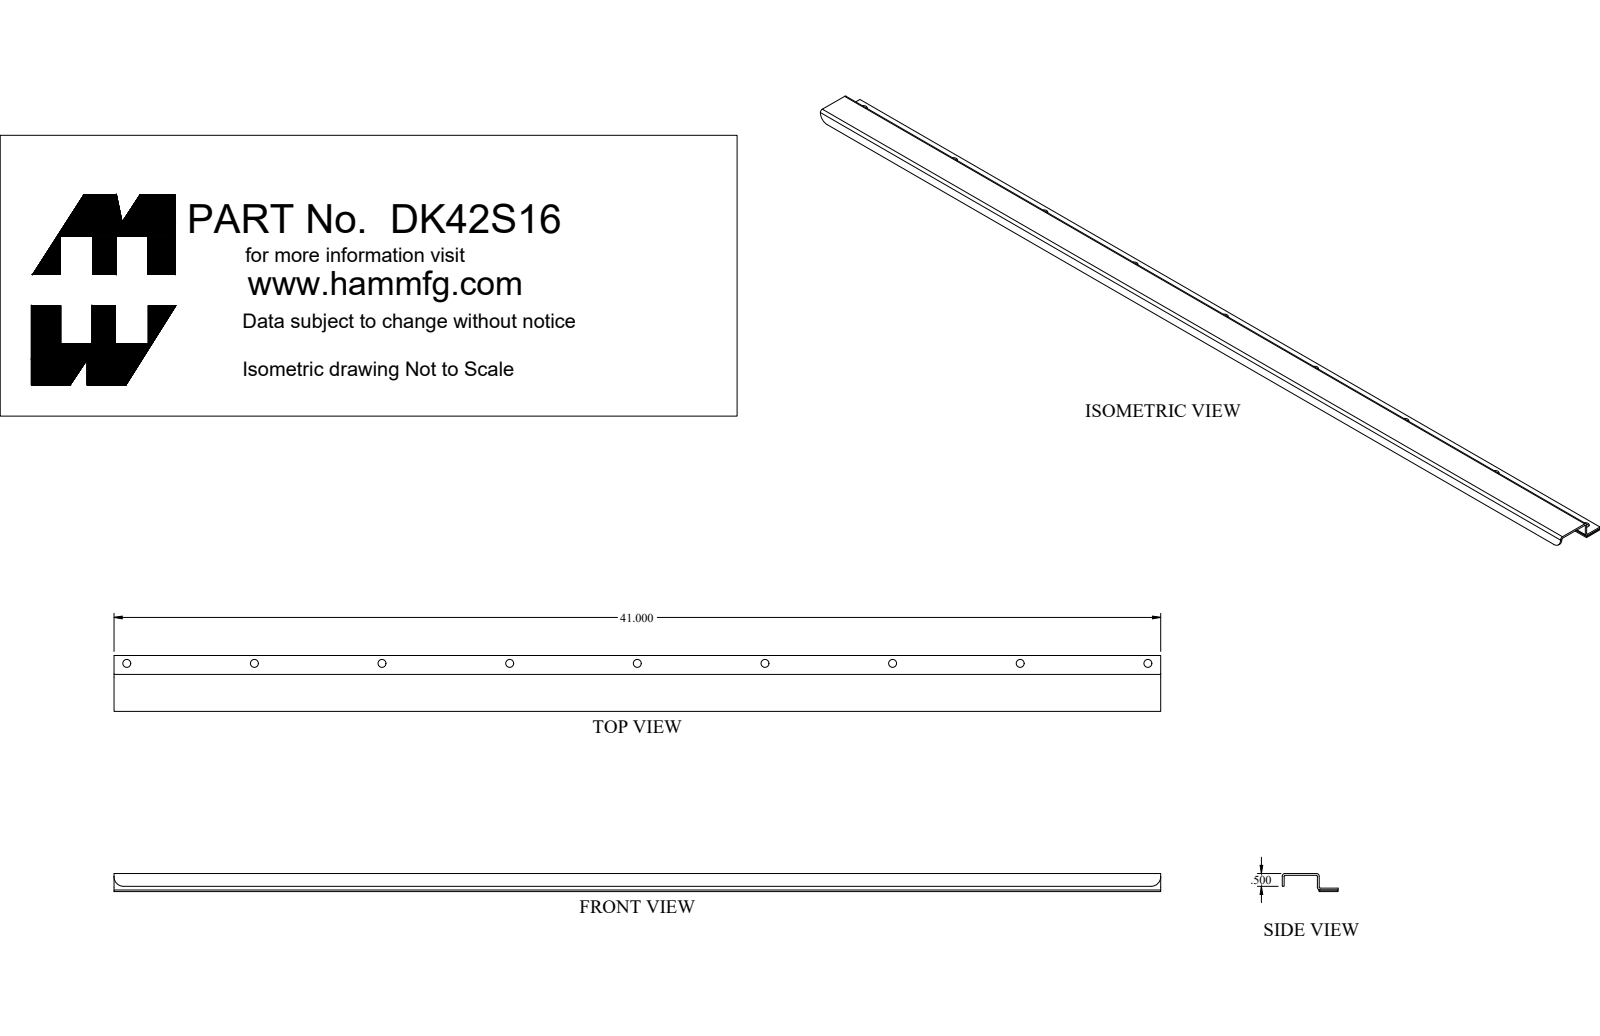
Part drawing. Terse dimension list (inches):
name: DK42S16
written by: SolidWorks 2021 (AUTOMOTIVE_DESIGN)
unit: in
bodies: 5 solids, 70 faces (47 planar, 22 cylindrical, 1 other)
size: 41 × 2.188 × 1.322
volume: 11.11 in³; area: 328.6 in²
holes: 9× ⌀0.313, 1× ⌀0.196, 1× ⌀0.275
bosses: 1× ⌀0.625, 1× ⌀0.483, 1× ⌀0.25
rounds: 3× R0.036, 3× R0.108, 2× R0.375
face distances: 0.072, 0.572, 0.644, 0.063, 1.376, 0.5, 0.635, 0.707, 0.135, 1.448
hole spacings: 5, 10, 15, 20, 25, 30, 35, 40
